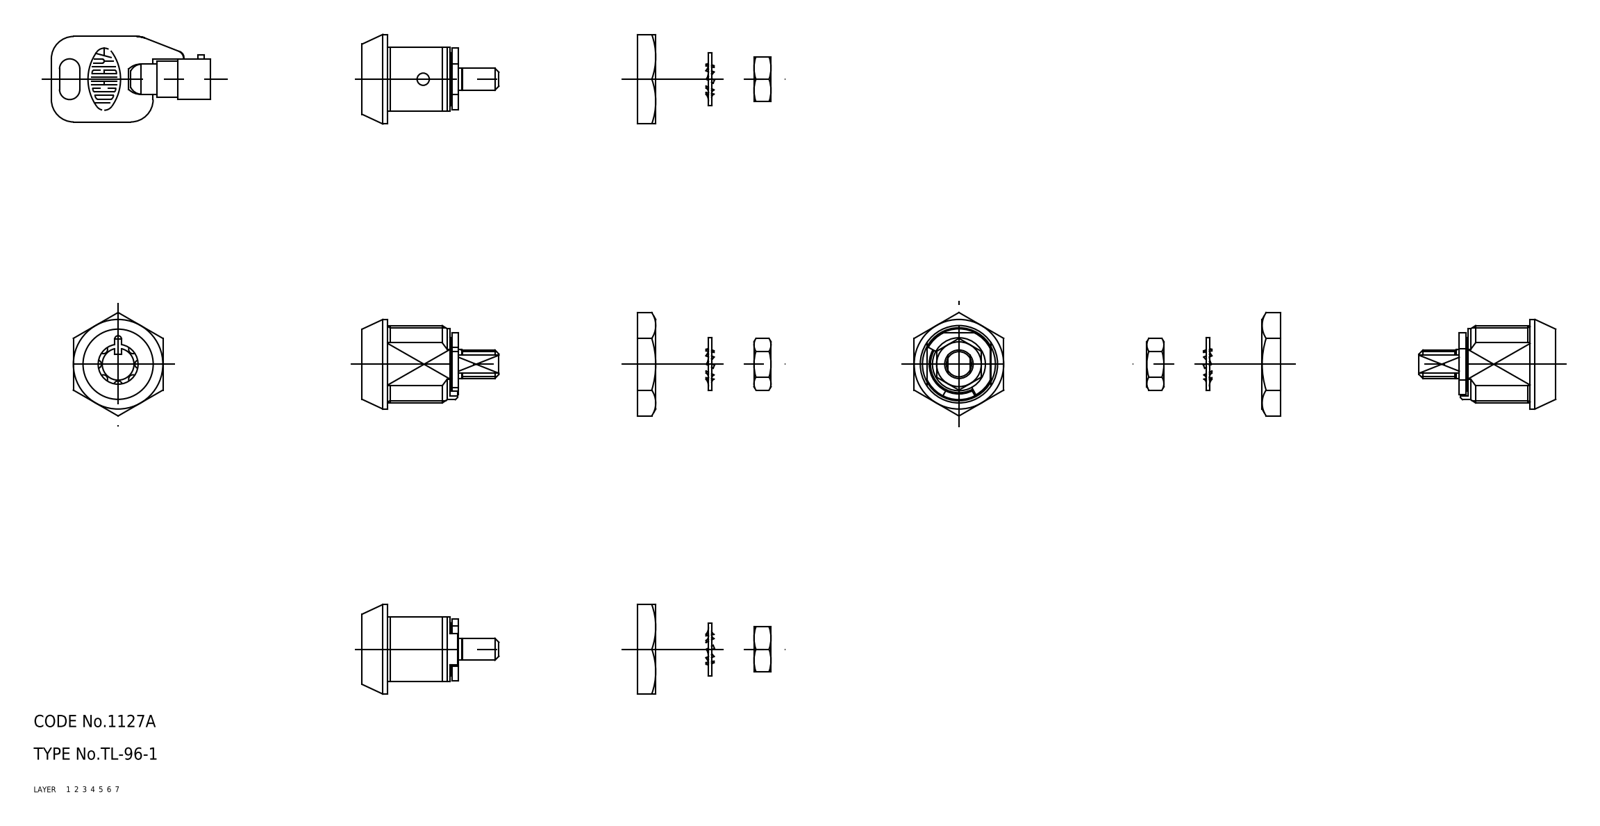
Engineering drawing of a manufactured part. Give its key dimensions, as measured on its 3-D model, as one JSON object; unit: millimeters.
{"part_name": "nut_B; nut_A; lock; key (+1 more)", "step_written_by": "CADfix (AUTOMOTIVE_DESIGN)", "units": "millimeters", "bodies": {"solids": 4, "faces": 142, "planar": 0, "cylindrical": 0, "other": 142}, "overall_size": [117.09, 25.4, 22], "volume_mm3": 8836, "surface_area_mm2": 6298}
